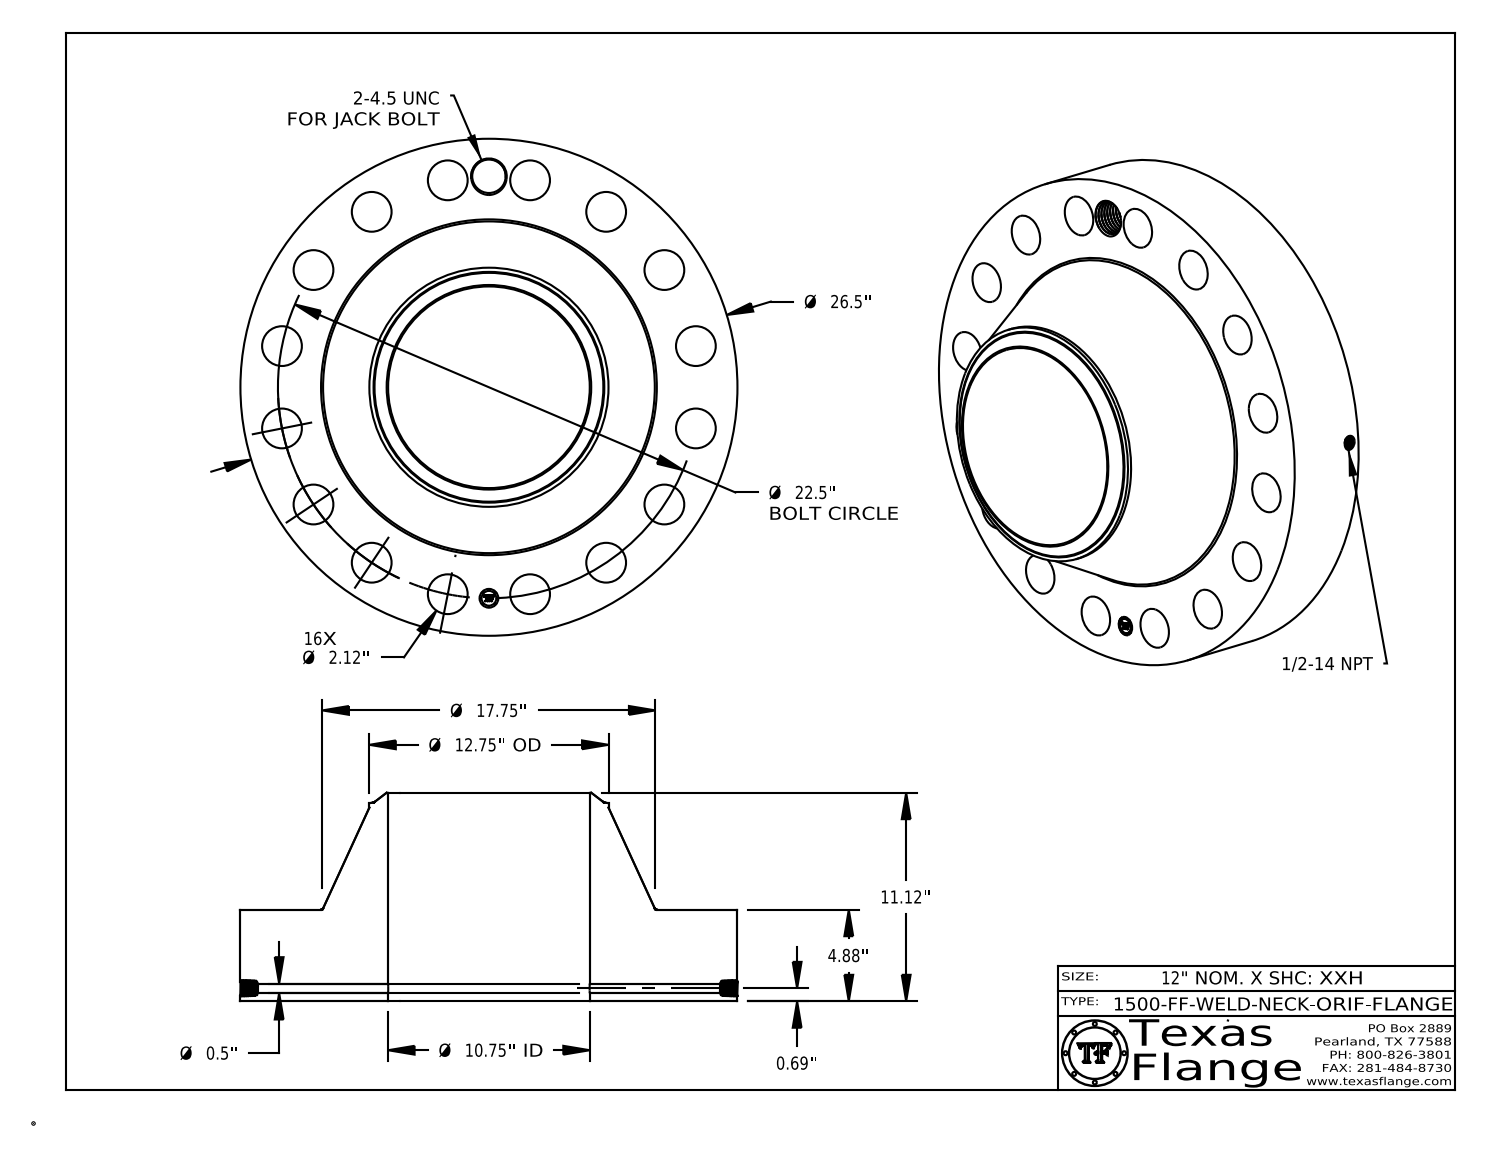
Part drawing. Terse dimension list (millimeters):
name: 1500-FF-WELD-NECK
written by: CATIA V5 STEP AP214 (AUTOMOTIVE_DESIGN)
unit: mm
bodies: 1 solid, 828 faces (368 planar, 122 cylindrical, 338 other)
size: 673.1 × 673.1 × 282.4
volume: 40 690 000 mm³; area: 1 520 000 mm²
holes: 16× ⌀53.8, 1× ⌀12.7, 1× ⌀17.1, 1× ⌀25.4, 1× ⌀45.2, 1× ⌀273.1
bosses: 8× ⌀1.5, 1× ⌀673.1, 1× ⌀323.9, 1× ⌀20
face distances: 124, 282.4, 158.5, 123.6, 0.4, 158.9, 7.6, 7.4, 1.4, 6.3
hole spacings: 285.8, 218.7, 404.1, 528, 317.5, 475.2, 560.5, 111.5
